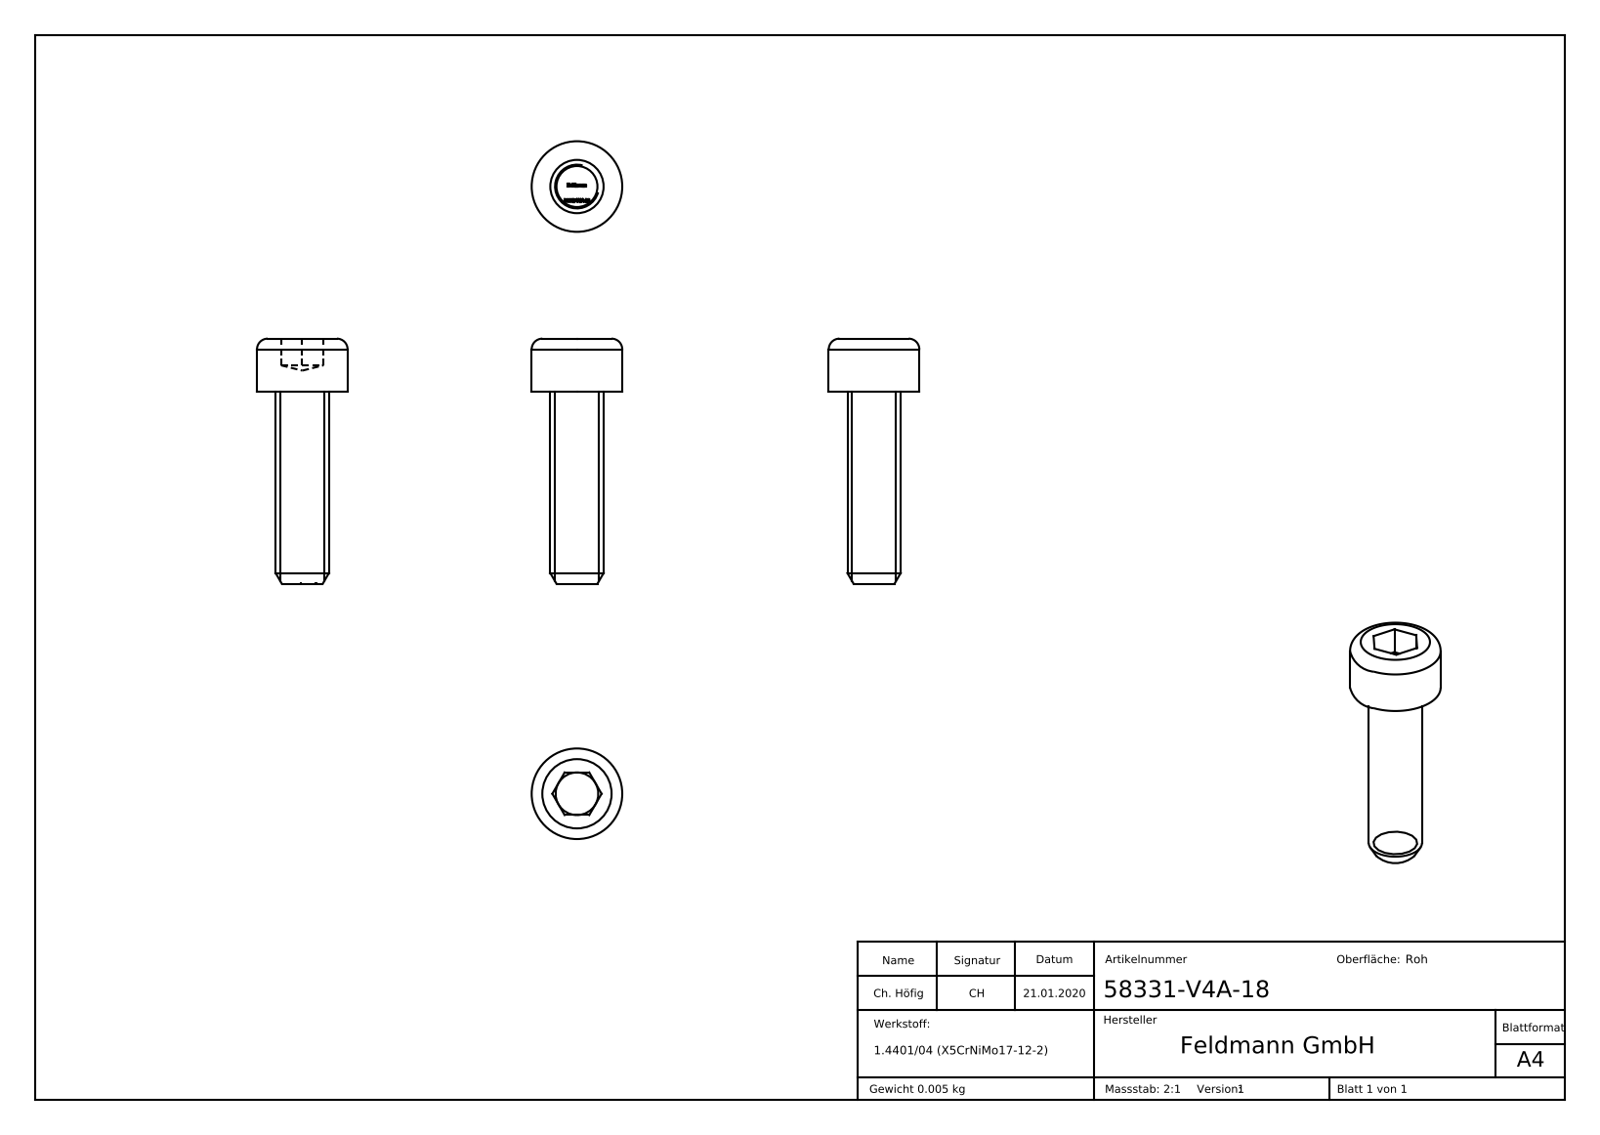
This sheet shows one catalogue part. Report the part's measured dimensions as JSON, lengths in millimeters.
{"part_name": "58331-V4A-18", "step_written_by": "SolidWorks 2015 (CONFIG_CONTROL_DESIGN)", "units": "millimeters", "bodies": {"solids": 1, "faces": 284, "planar": 161, "cylindrical": 2, "other": 121}, "overall_size": [24, 8.75, 8.5], "volume_mm3": 591, "surface_area_mm2": 547, "round_bosses_or_shafts": [[8.5, 1], [5, 1]], "face_to_face_distances": [5, 4, 18, 23, 2.5, 20.5, 17.9, 20.4, 22.9, 0.56]}
